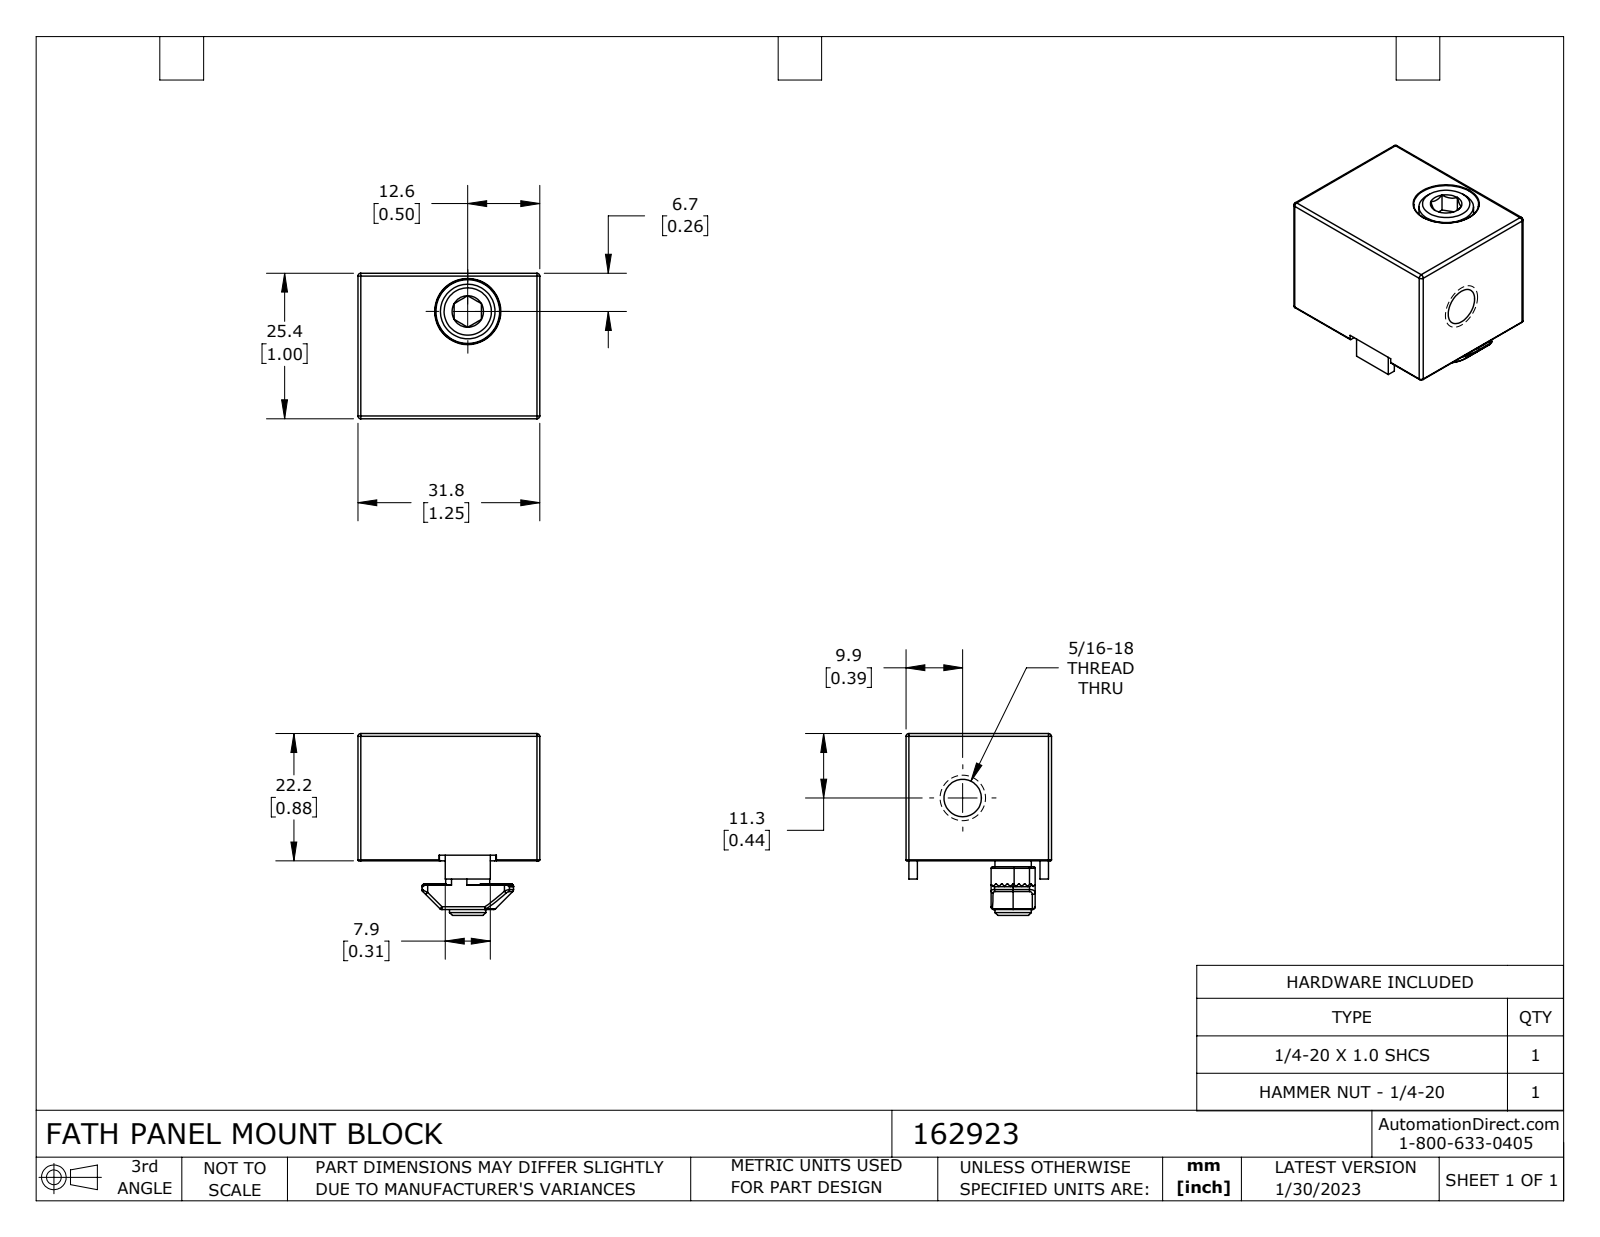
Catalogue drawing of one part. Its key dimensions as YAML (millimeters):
part_name: "162923"
step_written_by: "SolidWorks 2021 (CONFIG_CONTROL_DESIGN)"
units: millimeters
bodies: {solids: 2, faces: 261, planar: 110, cylindrical: 101, other: 50}
overall_size: [31.8, 31.8, 25.4]
volume: 13300
surface_area: 8258
round_holes:
  - {diameter: 4.7, count: 1}
  - {diameter: 6.5, count: 1}
round_bosses_or_shafts:
  - {diameter: 9.5, count: 1}
  - {diameter: 6.4, count: 1}
partial_cylinders:
  - {radius: 0.5, count: 18}
  - {radius: 0.2, count: 10}
  - {radius: 0.1, count: 7}
  - {radius: 1, count: 6}
  - {radius: 0.3, count: 4}
  - {radius: 2.1, count: 4}
  - {radius: 4, count: 2}
  - {radius: 5.3, count: 1}
face_to_face_distances: [2, 25.4, 31.8, 23.4, 29.7, 22.2, 21.4, 8.4, 24.1, 7.7]
